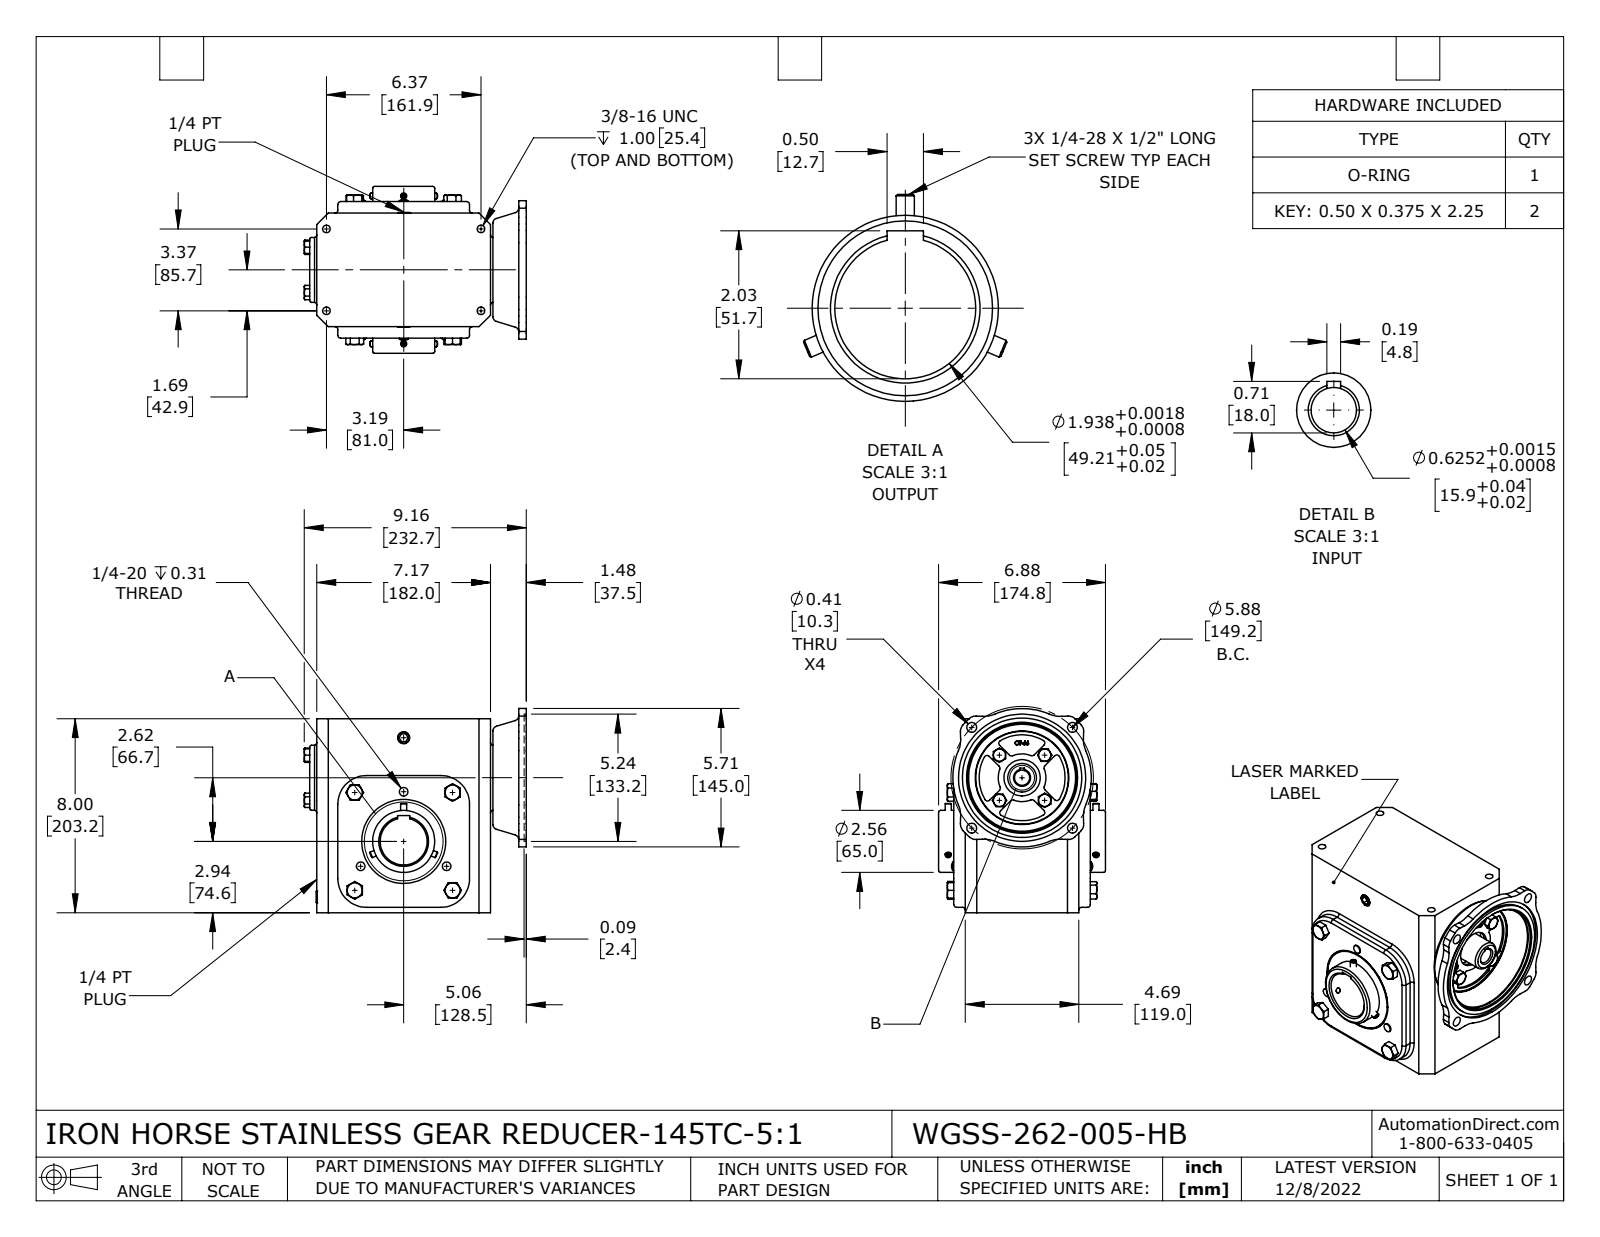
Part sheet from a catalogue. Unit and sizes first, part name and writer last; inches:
Units: inches
Overall size (bounding box): 9.16 × 8.417 × 6.882
Round holes (diameter × count): ⌀0.213 ×6, ⌀0.313 ×4, ⌀0.406 ×4, ⌀0.625 ×1, ⌀0.866 ×1, ⌀1.496 ×1, ⌀1.772 ×1, ⌀1.937 ×1, ⌀2.047 ×1, ⌀3.819 ×1, ⌀4.5 ×1, ⌀5.244 ×1
Round bosses / shafts (diameter × count): ⌀0.25 ×6, ⌀0.354 ×3, ⌀4.921 ×1, ⌀3.465 ×1, ⌀2.559 ×1, ⌀1.181 ×1
Partial cylindrical surfaces — rounded edges, fillets, slot ends (radius × count): R0.118 ×40, R0.394 ×12, R1.181 ×12, R0.079 ×4, R0.984 ×1, R1.772 ×1, R2.854 ×1, R3.27 ×1
Main face-to-face distances: 0.472, 5.157, 8, 7.165, 4.685, 5.63, 7.461, 7.71, 0.295, 1.161
Hole centre spacings: 2.937, 3.465, 4.154, 5.707, 6.094, 3.375, 5.875, 6.375
Volume: 289.1 in³ · Surface area: 423.6 in²
Bodies: 7 solids, 669 faces (285 planar, 191 cylindrical, 193 other)
Part name (STEP PRODUCT): WGSS-262-005-HB
STEP written by: SolidWorks 2021 (CONFIG_CONTROL_DESIGN)
